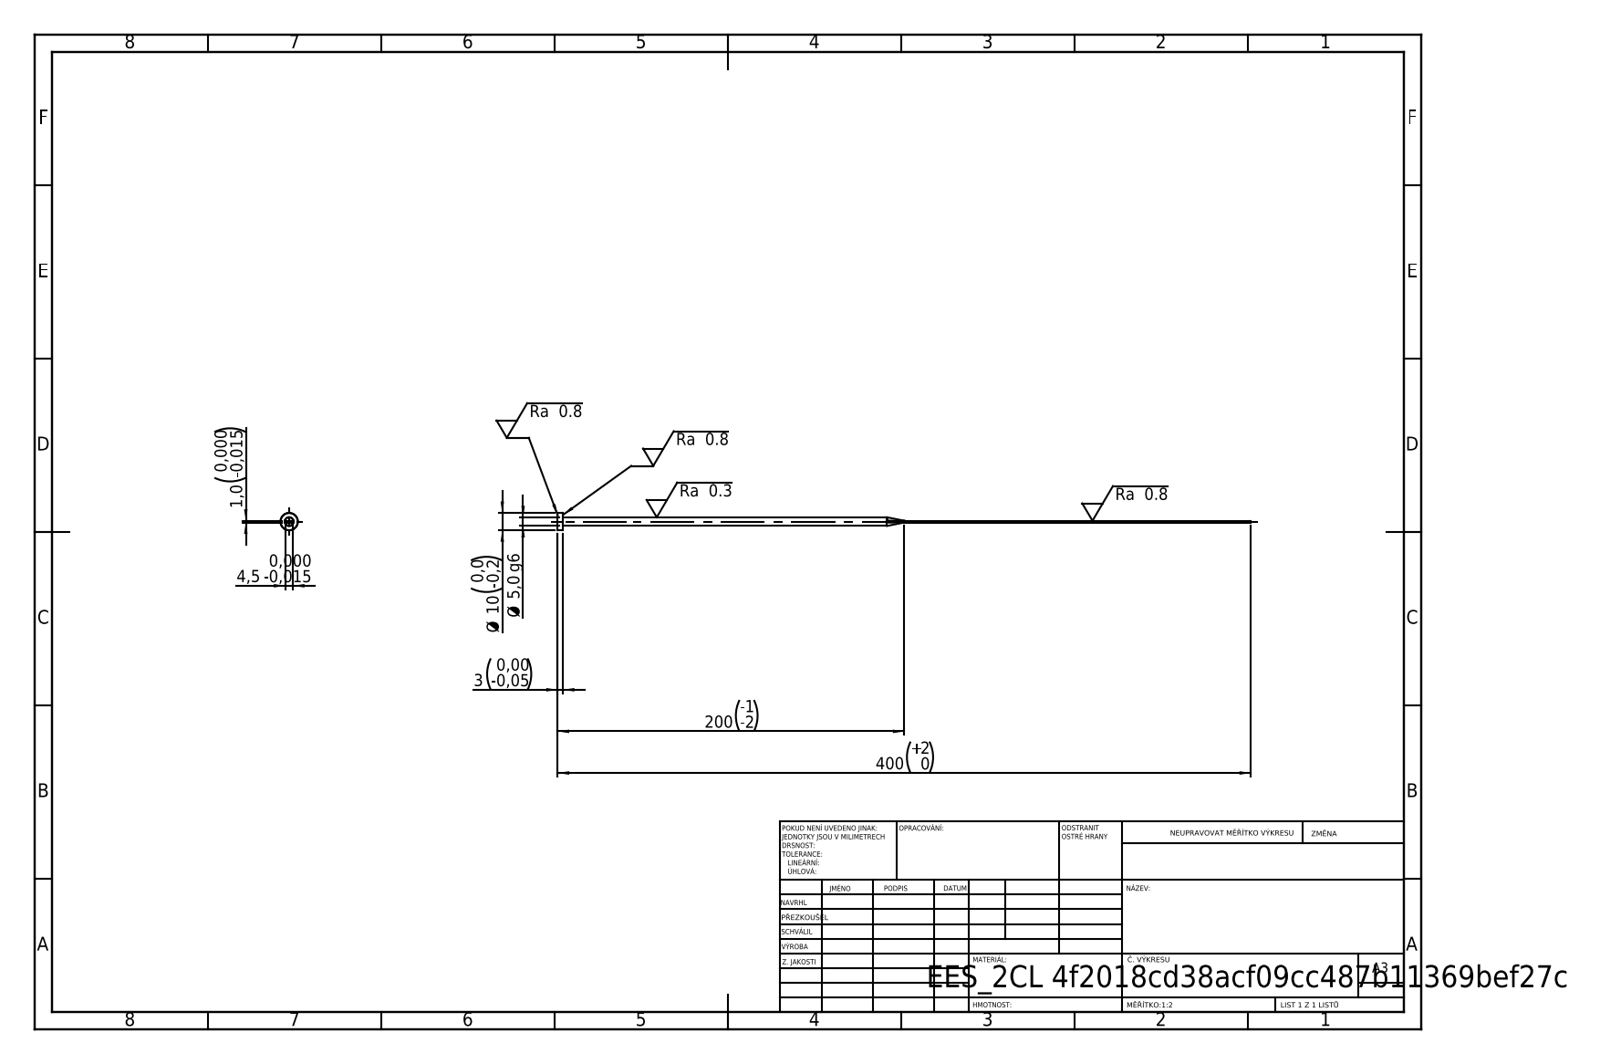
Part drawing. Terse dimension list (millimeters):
written by: SolidWorks 2019 (CONFIG_CONTROL_DESIGN)
unit: mm
bodies: 1 solid, 15 faces (7 planar, 4 cylindrical, 4 other)
size: 400 × 10 × 10
volume: 4 922 mm³; area: 5 503 mm²
bosses: 1× ⌀10, 1× ⌀5
face distances: 1, 4.5, 3, 400, 397
